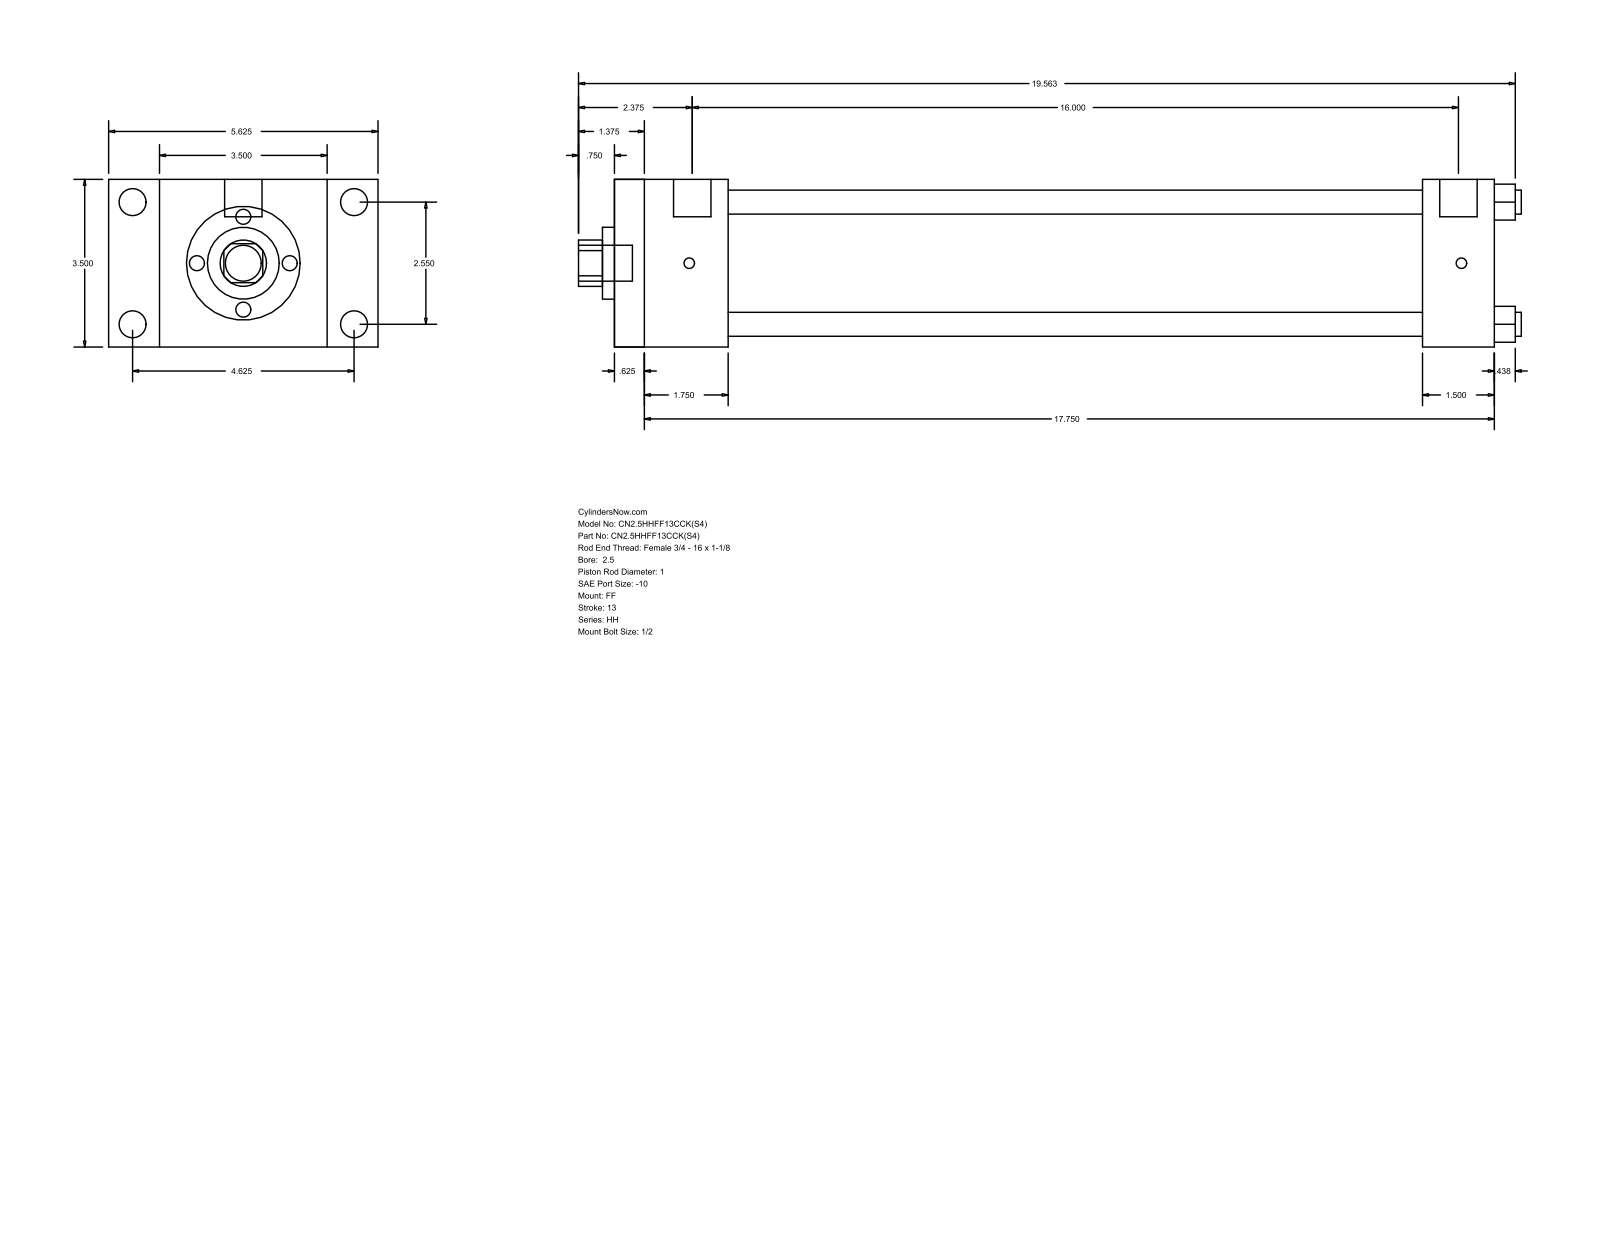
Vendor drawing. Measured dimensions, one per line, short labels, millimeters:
name: HH_FF__0250_1
written by: GSSL Pune (CONFIG_CONTROL_DESIGN)
unit: mm
bodies: 0 solids, 92 faces (64 planar, 28 cylindrical, 0 other)
size: 500.06 × 142.88 × 88.9
holes: 4× ⌀12.7, 1× ⌀25.4, 1× ⌀38.1, 1× ⌀73.03
bosses: 4× ⌀14.3, 4× ⌀5.56, 2× ⌀19.84, 1× ⌀19.05
rounds: 1× R12.29
face distances: 88.9, 466.72, 15.87, 450.85, 60.33, 44.46, 406.39, 428.63, 412.76, 368.3
hole spacings: 45.79, 64.76, 91.58
